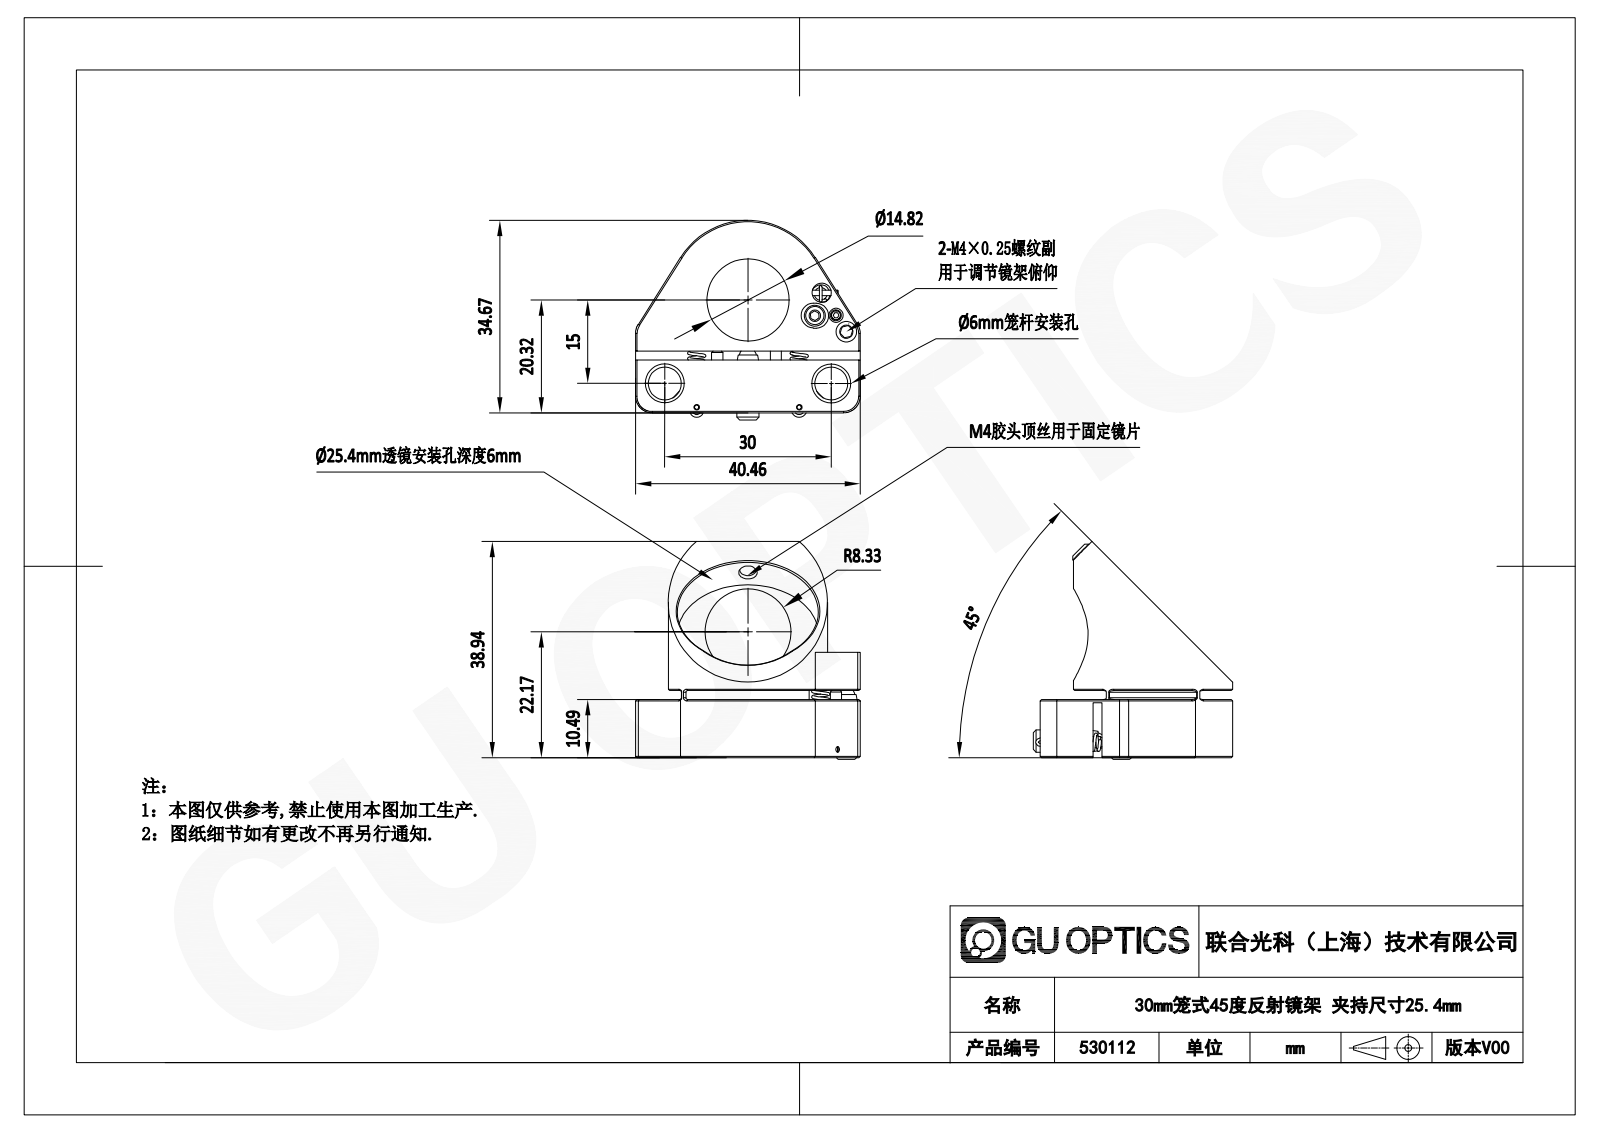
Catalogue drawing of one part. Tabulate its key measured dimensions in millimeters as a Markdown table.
| quantity | value |
| --- | --- |
| part name | 530112 |
| STEP written by | SolidWorks 2020 (CONFIG_CONTROL_DESIGN) |
| units | millimeters |
| bodies | 18 solids, 321 faces (151 planar, 67 cylindrical, 103 other) |
| overall size | 40.47 × 39.22 × 35.92 |
| volume | 13 178 mm³ |
| surface area | 10 701 mm² |
| round holes (diameter × count) | 1.6 × 4, 1 × 3, 2.8 × 3, 3.3 × 3, 3.5 × 3, 2.99 × 2, 3.75 × 2, 6 × 2, 14.82 × 1, 16.66 × 1 |
| round bosses / shafts (diameter × count) | 4 × 5, 2 × 4, 3.8 × 2, 28.7 × 1, 3 × 1, 1 × 1 |
| partial cylindrical surfaces (radius × count) | 0.3 × 4, 2.25 × 4, 3 × 4, 1.25 × 2, 1.3 × 2, 2 × 1, 5 × 1, 10.5 × 1 |
| main face-to-face distances | 10.49, 12.09, 1.6, 1.59, 9.53, 11.12, 5.97, 40.46, 18.99, 8.5 |
| hole center spacings | 4.22, 7.21, 20.14, 9.23, 12.37, 18.46, 21.21, 21.41 |
